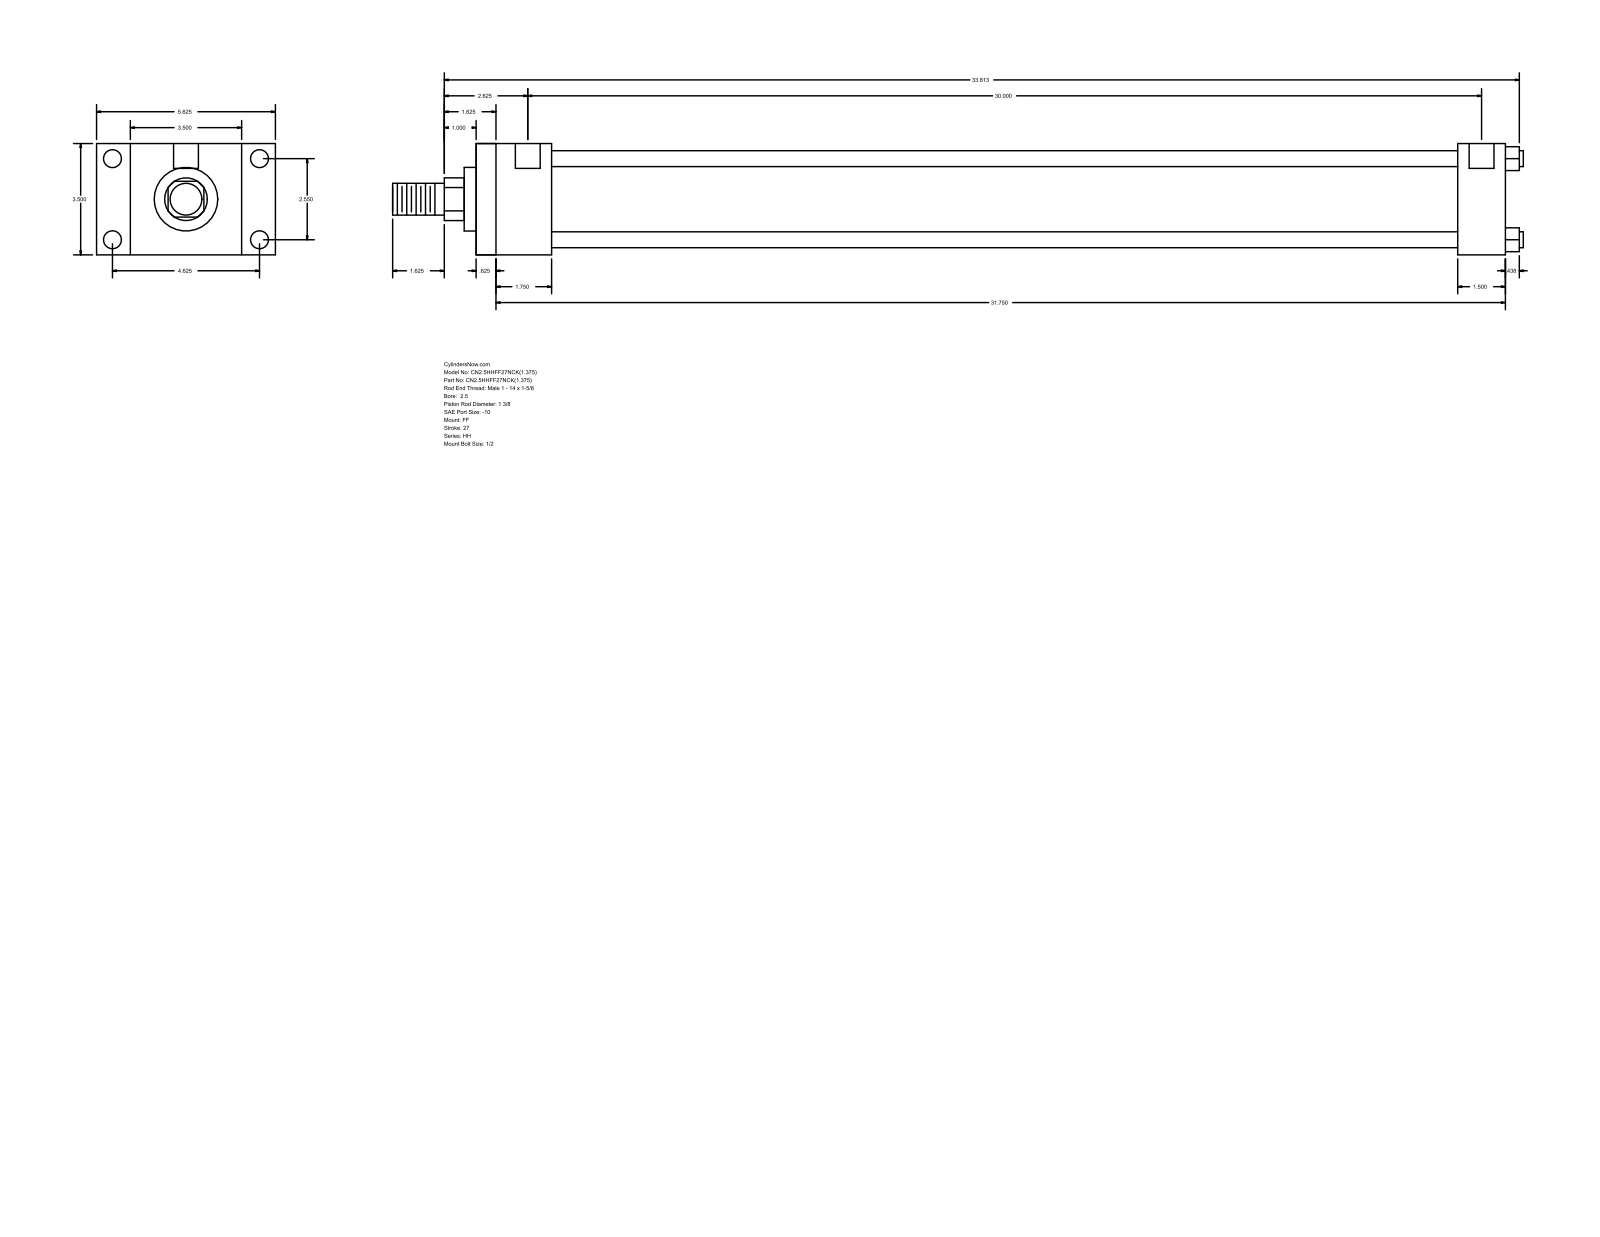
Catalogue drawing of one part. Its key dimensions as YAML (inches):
part_name: "HH_FF__0250_1.375"
step_written_by: "GSSL Pune (CONFIG_CONTROL_DESIGN)"
units: inches
bodies: {solids: 0, faces: 92, planar: 64, cylindrical: 28, other: 0}
overall_size: [35.563, 5.625, 3.5]
round_holes:
  - {diameter: 0.219, count: 4}
  - {diameter: 0.563, count: 4}
  - {diameter: 0.781, count: 2}
round_bosses_or_shafts:
  - {diameter: 0.5, count: 4}
  - {diameter: 2.875, count: 1}
  - {diameter: 2, count: 1}
  - {diameter: 1.375, count: 1}
  - {diameter: 1, count: 1}
partial_cylinders:
  - {radius: 0.672, count: 1}
face_to_face_distances: [3.5, 32.375, 0.625, 31.75, 2.375, 1.75, 30, 30.875, 30.25, 28.5]
hole_center_spacings: [2.55, 4.625, 5.281, 30.125, 0.062, 0.063, 30, 30.062]
